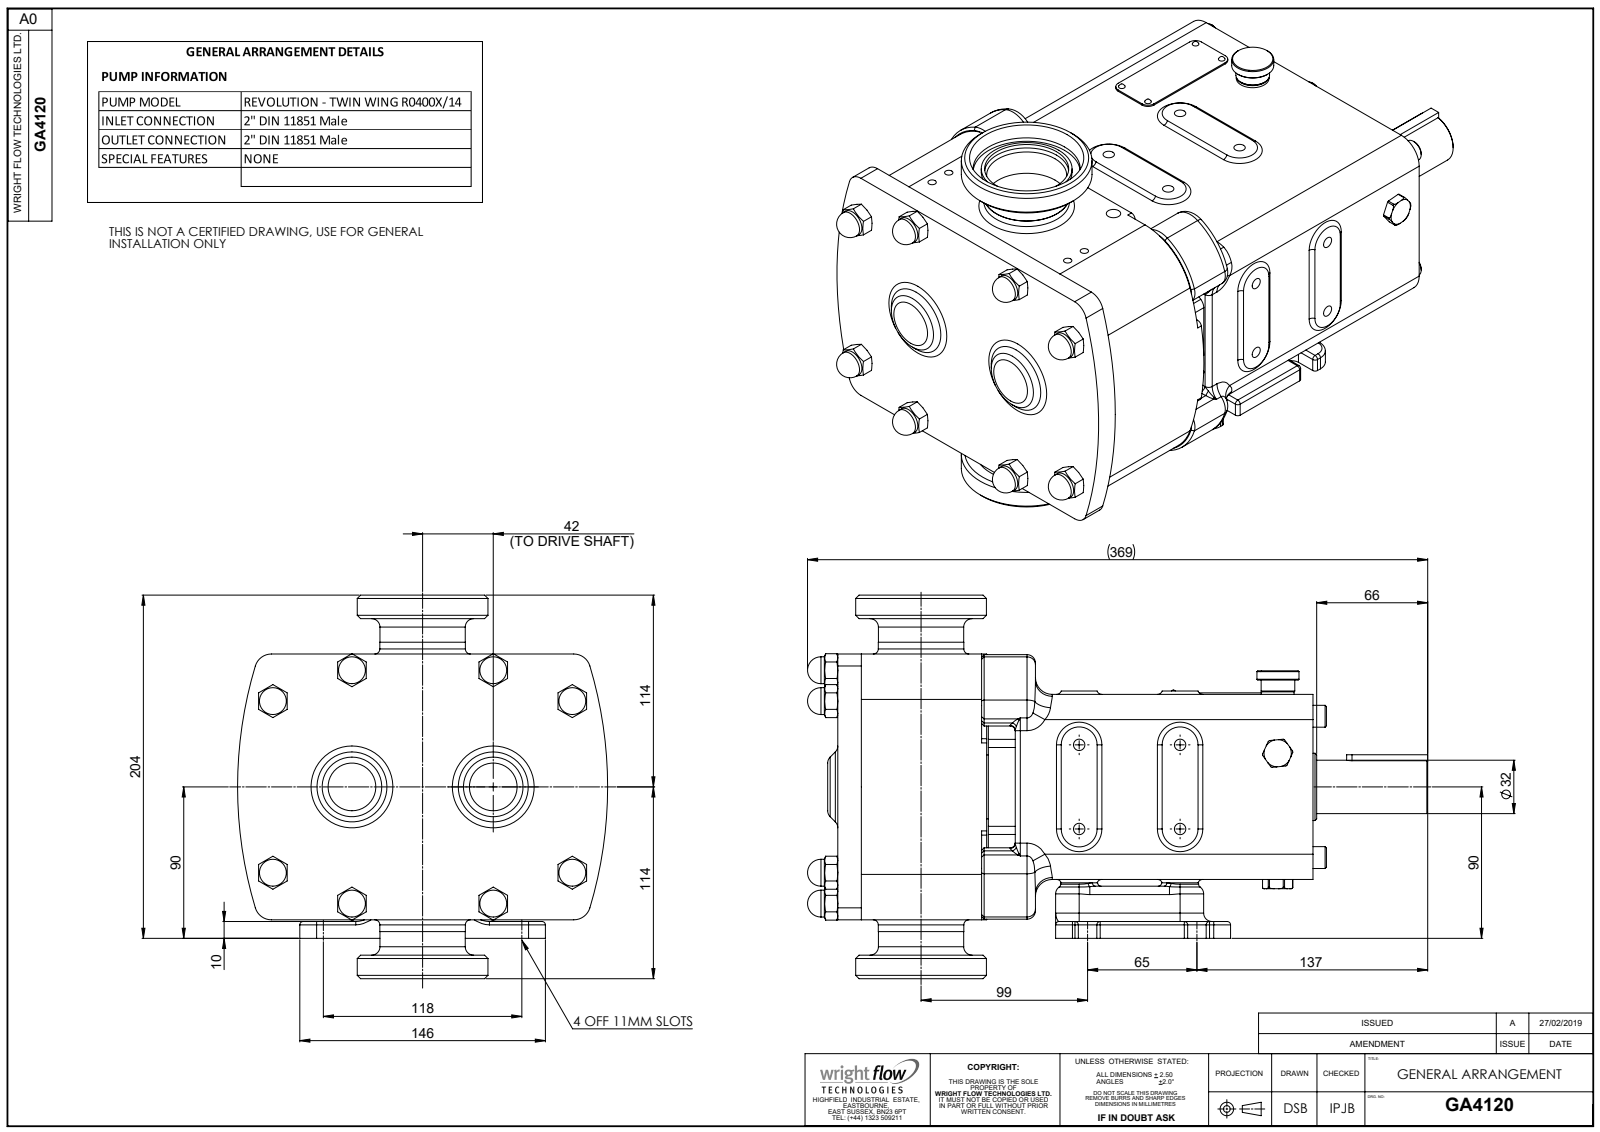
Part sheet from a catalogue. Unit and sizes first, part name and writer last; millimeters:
Units: millimetres
Overall size (bounding box): 368.7 × 228 × 220
Round holes (diameter × count): ⌀6.8 ×8, ⌀5 ×4, ⌀8.6 ×2, ⌀6 ×1, ⌀23 ×1, ⌀47.6 ×1, ⌀50 ×1, ⌀63.7 ×1
Round bosses / shafts (diameter × count): ⌀16 ×8, ⌀13 ×7, ⌀77.7 ×1, ⌀54 ×1, ⌀50.85 ×1, ⌀50.7 ×1, ⌀40 ×1, ⌀38 ×1
Partial cylindrical surfaces — rounded edges, fillets, slot ends (radius × count): R10 ×30, R3 ×28, R2 ×24, R5 ×19, R5.9 ×8, R15 ×8, R5.5 ×4, R8 ×4
Main face-to-face distances: 194, 24, 88.5, 1, 110, 282.5, 134, 193, 89.5, 145
Hole centre spacings: 50, 60, 78.1, 14, 42.25, 52.2, 55.56, 57.63
Volume: 7 378 000 mm³ · Surface area: 388 591 mm²
Bodies: 3 solids, 962 faces (296 planar, 312 cylindrical, 354 other)
Part name (STEP PRODUCT): Copy of Z94-5031-33 - 2 INCH DIN11851^GA4120; Copy (2) of Z94-5031-33 - 2 INCH DIN11851^GA4120; GA4120; Copy of R0400 CPP V RHD^GA4120
STEP written by: SolidWorks 2023 (AUTOMOTIVE_DESIGN)
